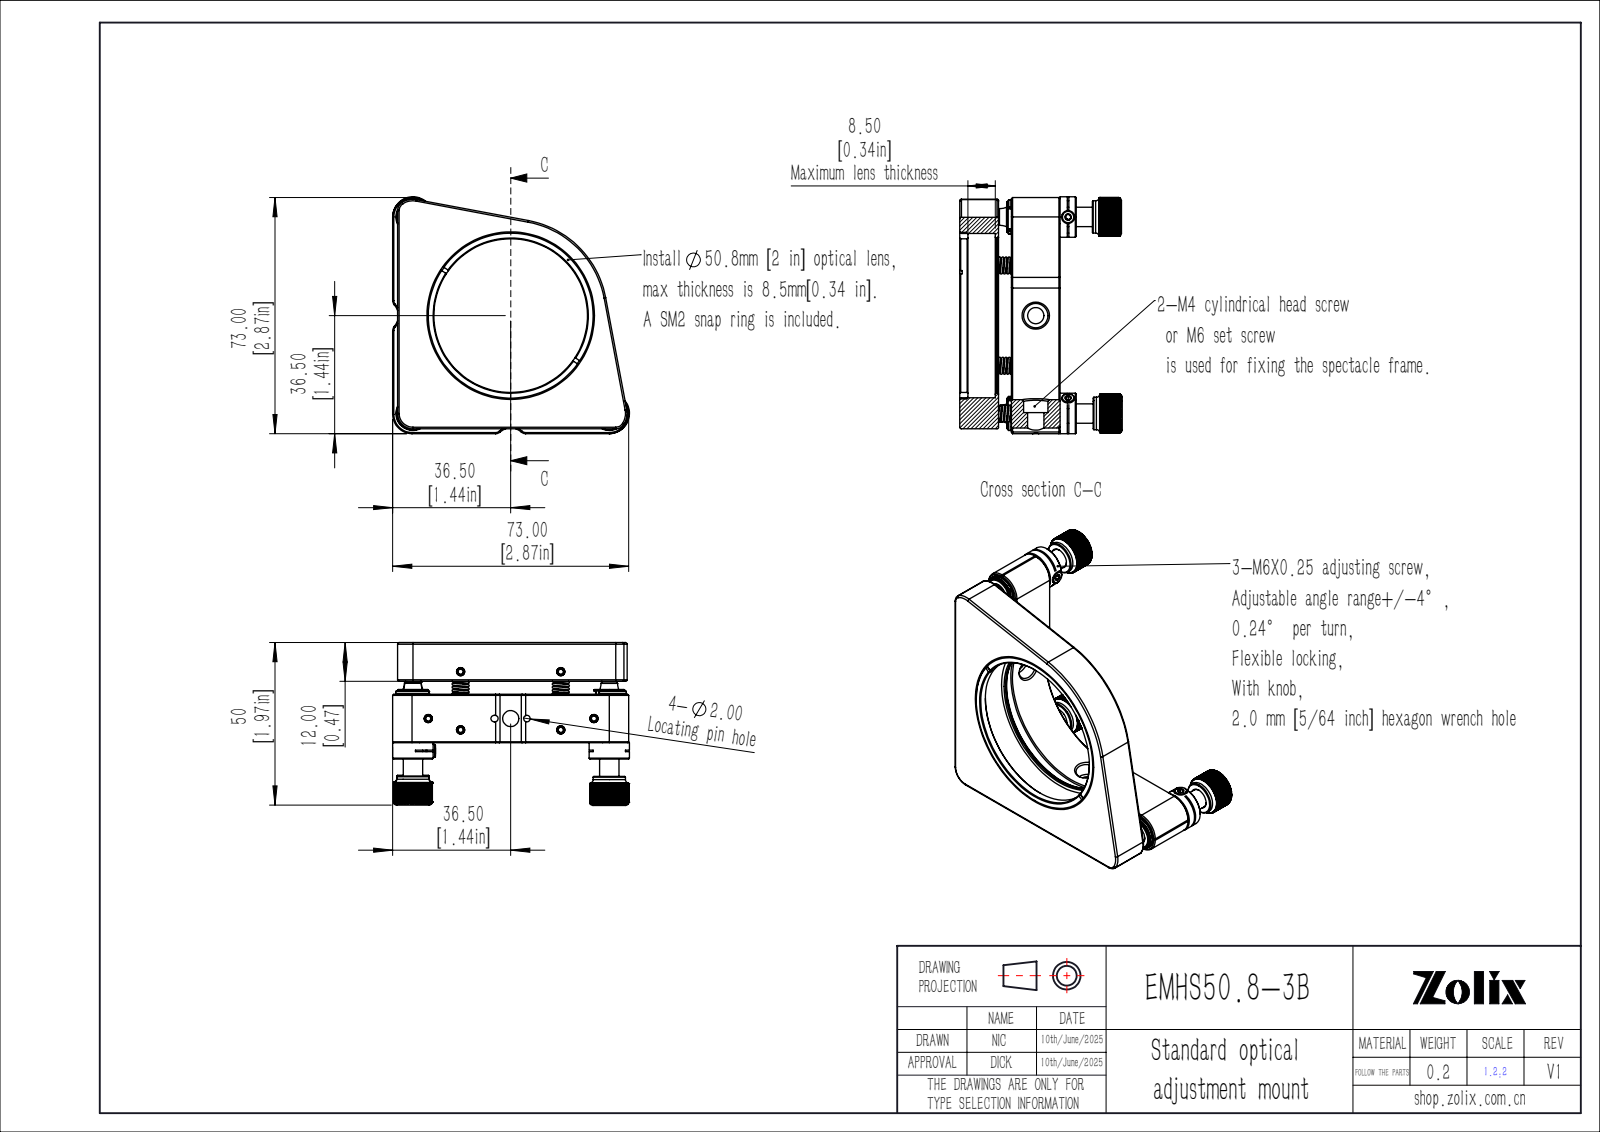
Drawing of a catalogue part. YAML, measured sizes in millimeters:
part_name: "EMHS50.8-3B"
step_written_by: "SolidWorks 2020 (CONFIG_CONTROL_DESIGN)"
units: millimeters
bodies: {solids: 0, faces: 1299, planar: 644, cylindrical: 375, other: 280}
overall_size: [73.25, 73.25, 50.37]
round_holes:
  - {diameter: 6, count: 4}
  - {diameter: 3, count: 2}
  - {diameter: 10, count: 2}
  - {diameter: 4, count: 1}
  - {diameter: 4.6, count: 1}
  - {diameter: 6.3, count: 1}
  - {diameter: 10.5, count: 1}
  - {diameter: 47.5, count: 1}
  - {diameter: 48, count: 1}
  - {diameter: 50.8, count: 1}
round_bosses_or_shafts:
  - {diameter: 3, count: 6}
  - {diameter: 4, count: 5}
  - {diameter: 12.5, count: 3}
  - {diameter: 9.5, count: 3}
  - {diameter: 8, count: 3}
  - {diameter: 6, count: 3}
  - {diameter: 7.5, count: 2}
  - {diameter: 5, count: 2}
partial_cylinders:
  - {radius: 0.5, count: 8}
  - {radius: 6, count: 8}
  - {radius: 0.8, count: 4}
  - {radius: 1, count: 4}
  - {radius: 2, count: 4}
  - {radius: 3, count: 2}
  - {radius: 5, count: 2}
  - {radius: 5.25, count: 2}
face_to_face_distances: [12, 1.5, 31, 19, 4, 15, 16, 11, 12.5, 5]
hole_center_spacings: [33.99, 31, 14.75, 15, 42.96, 45.75, 46, 48.07]
